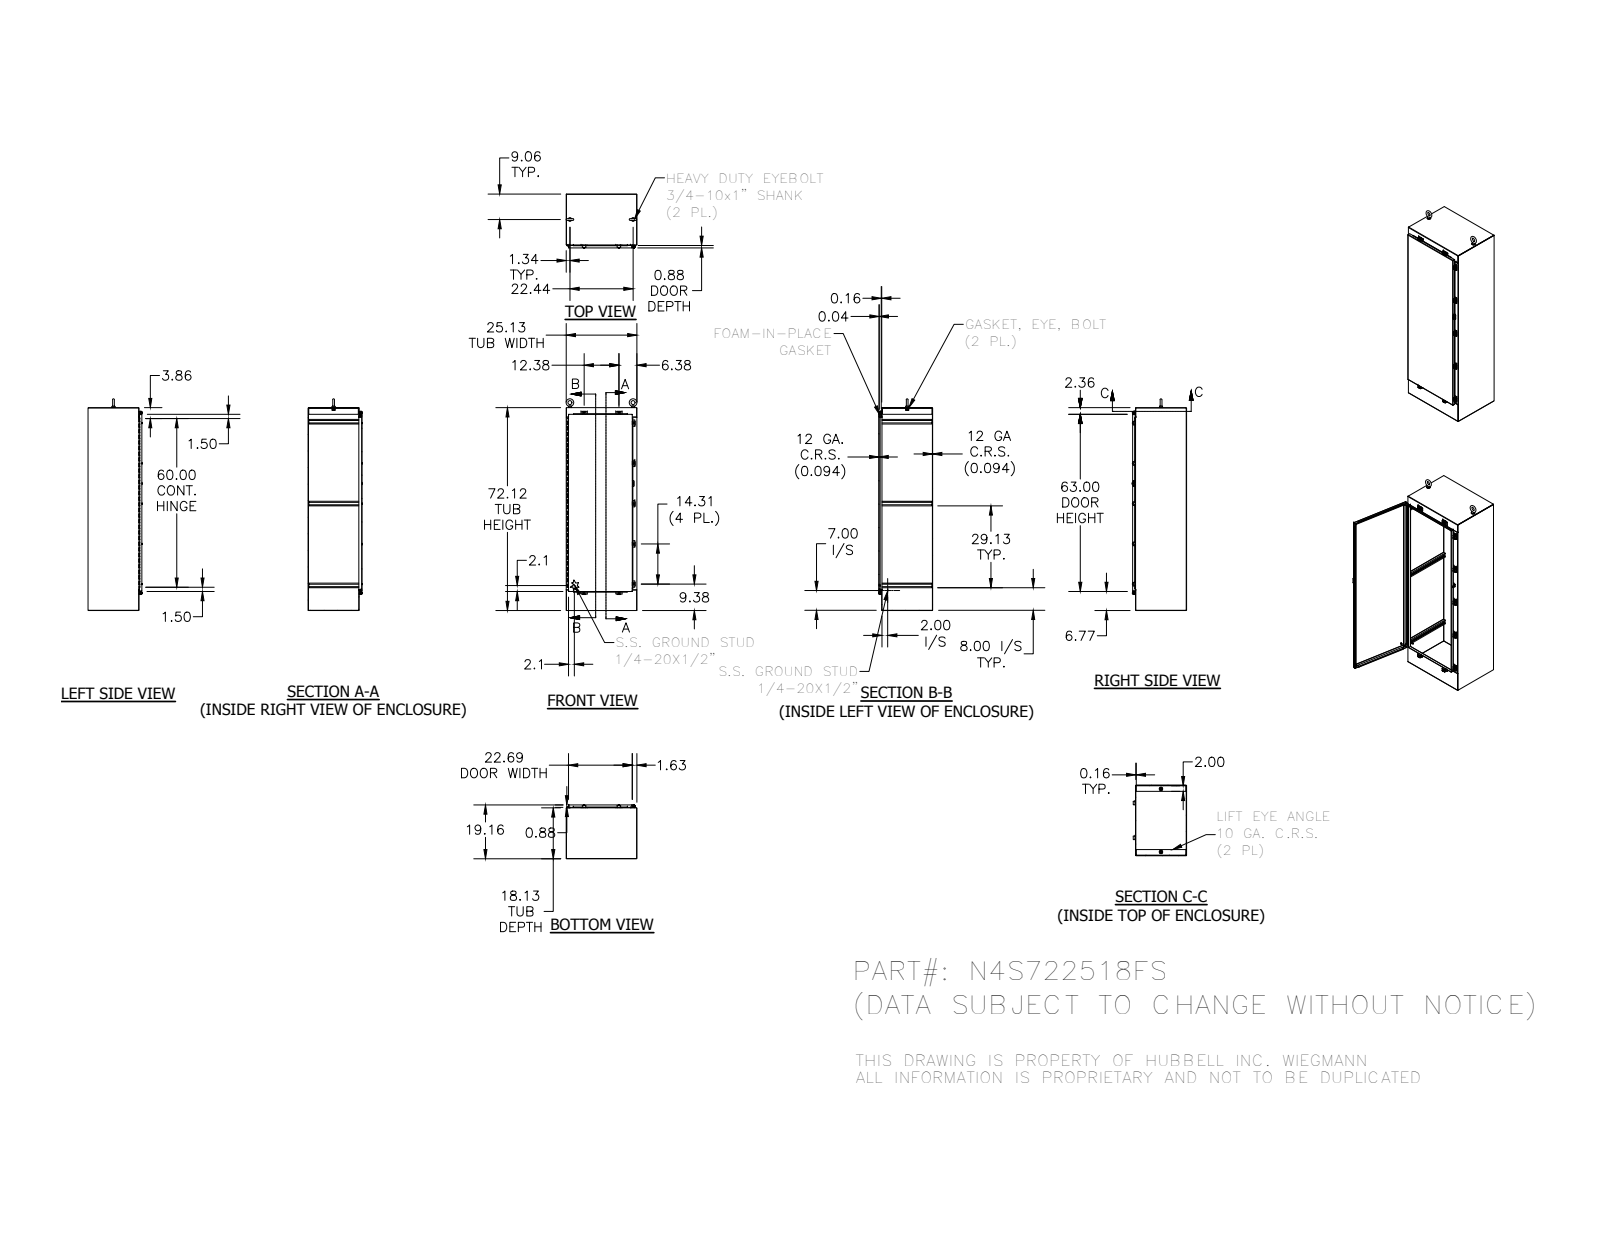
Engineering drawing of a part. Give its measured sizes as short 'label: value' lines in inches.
name: 38413_1; 30823_1; HSSN1300W60_1; HFW3025_1 (+8 more)
written by: SolidWorks 2014 (AUTOMOTIVE_DESIGN)
unit: in
bodies: 78 solids, 3000 faces (1210 planar, 1210 cylindrical, 580 other)
size: 75.248 × 25.125 × 19.355
volume: 861.7 in³; area: 17 693 in²
holes: 9× ⌀0.211, 9× ⌀0.281, 9× ⌀0.3, 3× ⌀0.11, 2× ⌀0.642, 2× ⌀0.813, 1× ⌀0.125, 1× ⌀0.156, 1× ⌀0.5
bosses: 12× ⌀0.25, 9× ⌀0.52, 9× ⌀0.5, 9× ⌀0.35, 2× ⌀1.25, 2× ⌀1.12, 2× ⌀0.75, 2× ⌀0.337
rounds: 107× R0.03, 43× R0.125, 22× R0.062, 21× R0.25, 19× R0.031, 18× R0.019, 18× R0.053, 18× R0.086
face distances: 0.094, 19.067, 25.031, 18.973, 19.161, 24.938, 25.125, 18.031, 1.035, 72.031
hole spacings: 14.313, 28.626, 0.789, 12.38, 42.939, 64.375, 65.554, 0.449
